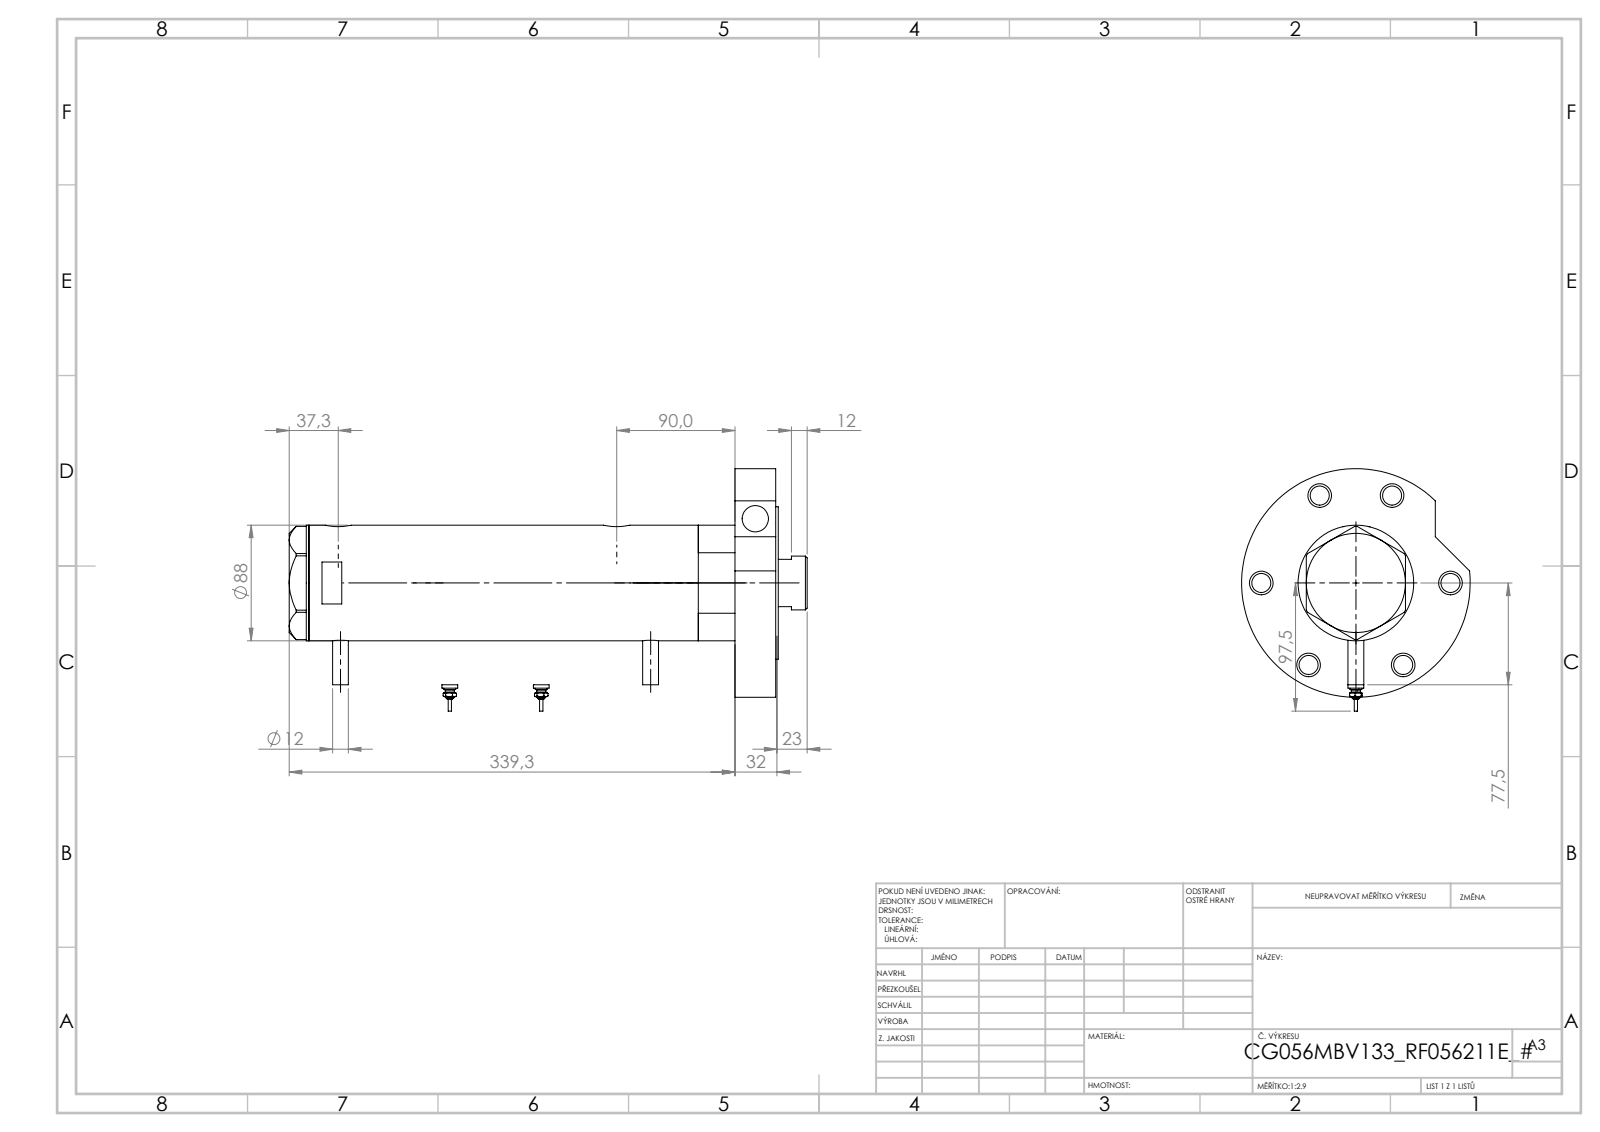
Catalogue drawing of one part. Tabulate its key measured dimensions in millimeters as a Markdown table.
| quantity | value |
| --- | --- |
| part name | V270CG_MIDDLE; Switch; V270CG_BACK; V270CG_FRONT (+2 more) |
| STEP written by | SolidWorks 2019 (CONFIG_CONTROL_DESIGN) |
| units | millimeters |
| bodies | 7 solids, 257 faces (91 planar, 102 cylindrical, 64 other) |
| overall size | 394.3 × 184.5 × 174 |
| volume | 2 579 000 mm³ |
| surface area | 361 439 mm² |
| round holes (diameter × count) | 14.5 × 7, 18 × 6, 20 × 3, 12.5 × 2, 13.16 × 2, 42 × 1, 43.5 × 1, 56 × 1, 60 × 1, 75 × 1, 80 × 1 |
| round bosses / shafts (diameter × count) | 12 × 4, 9 × 2, 7 × 2, 4.5 × 2, 2.5 × 2, 174 × 1, 116 × 1, 88 × 1 |
| main face-to-face distances | 31, 2, 357.3, 324.3, 355.3, 33, 234.4, 89.9, 120.9, 122.9 |
| hole center spacings | 72, 80, 119.73, 124.71, 129.15, 143.69, 1.7, 25.8 |
